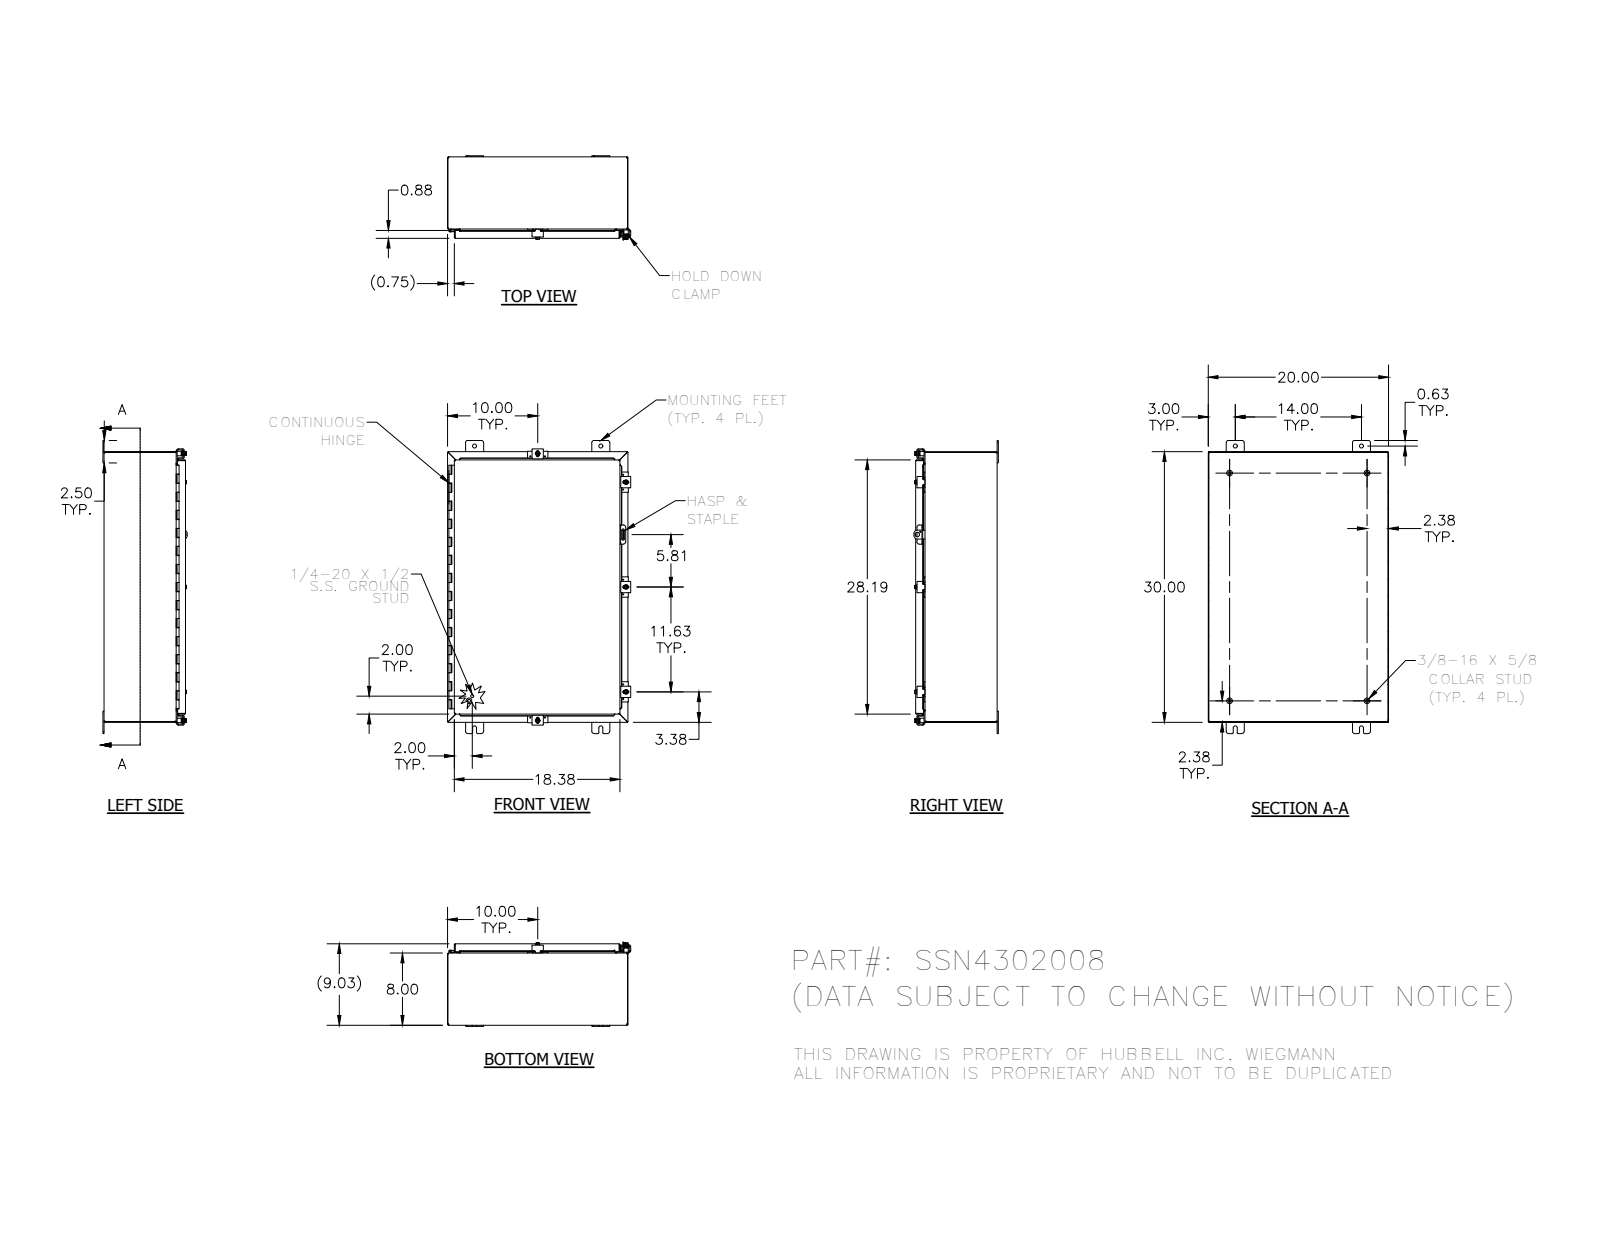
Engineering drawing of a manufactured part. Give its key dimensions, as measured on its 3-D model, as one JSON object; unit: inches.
{"part_name": "30824; 30818; 32912; SSN4302008BKP (+8 more)", "step_written_by": "SolidWorks 2014 (AUTOMOTIVE_DESIGN)", "units": "inches", "bodies": {"solids": 42, "faces": 1743, "planar": 683, "cylindrical": 773, "other": 287}, "overall_size": [32.5, 20.311, 9.355], "volume_in3": 182.2, "surface_area_in2": 4788, "round_holes": [[0.11, 10], [0.211, 5], [0.281, 5], [0.3, 5], [0.438, 4], [0.125, 1], [0.156, 1], [0.5, 1]], "round_bosses_or_shafts": [[0.25, 7], [0.52, 5], [0.5, 5], [0.35, 5], [0.625, 4], [0.33, 4], [0.115, 2], [0.337, 1]], "partial_cylinders_radius": [[0.03, 61], [0.125, 35], [0.25, 31], [0.031, 23], [0.105, 23], [0.062, 13], [0.141, 10], [0.07, 8]], "face_to_face_distances": [0.074, 8.959, 8.885, 9.033, 19.926, 29.926, 7.926, 1.033, 19.852, 20], "hole_center_spacings": [0.876, 29.3, 1.625, 10.818, 11.625, 11.625, 12.442, 23.25]}
